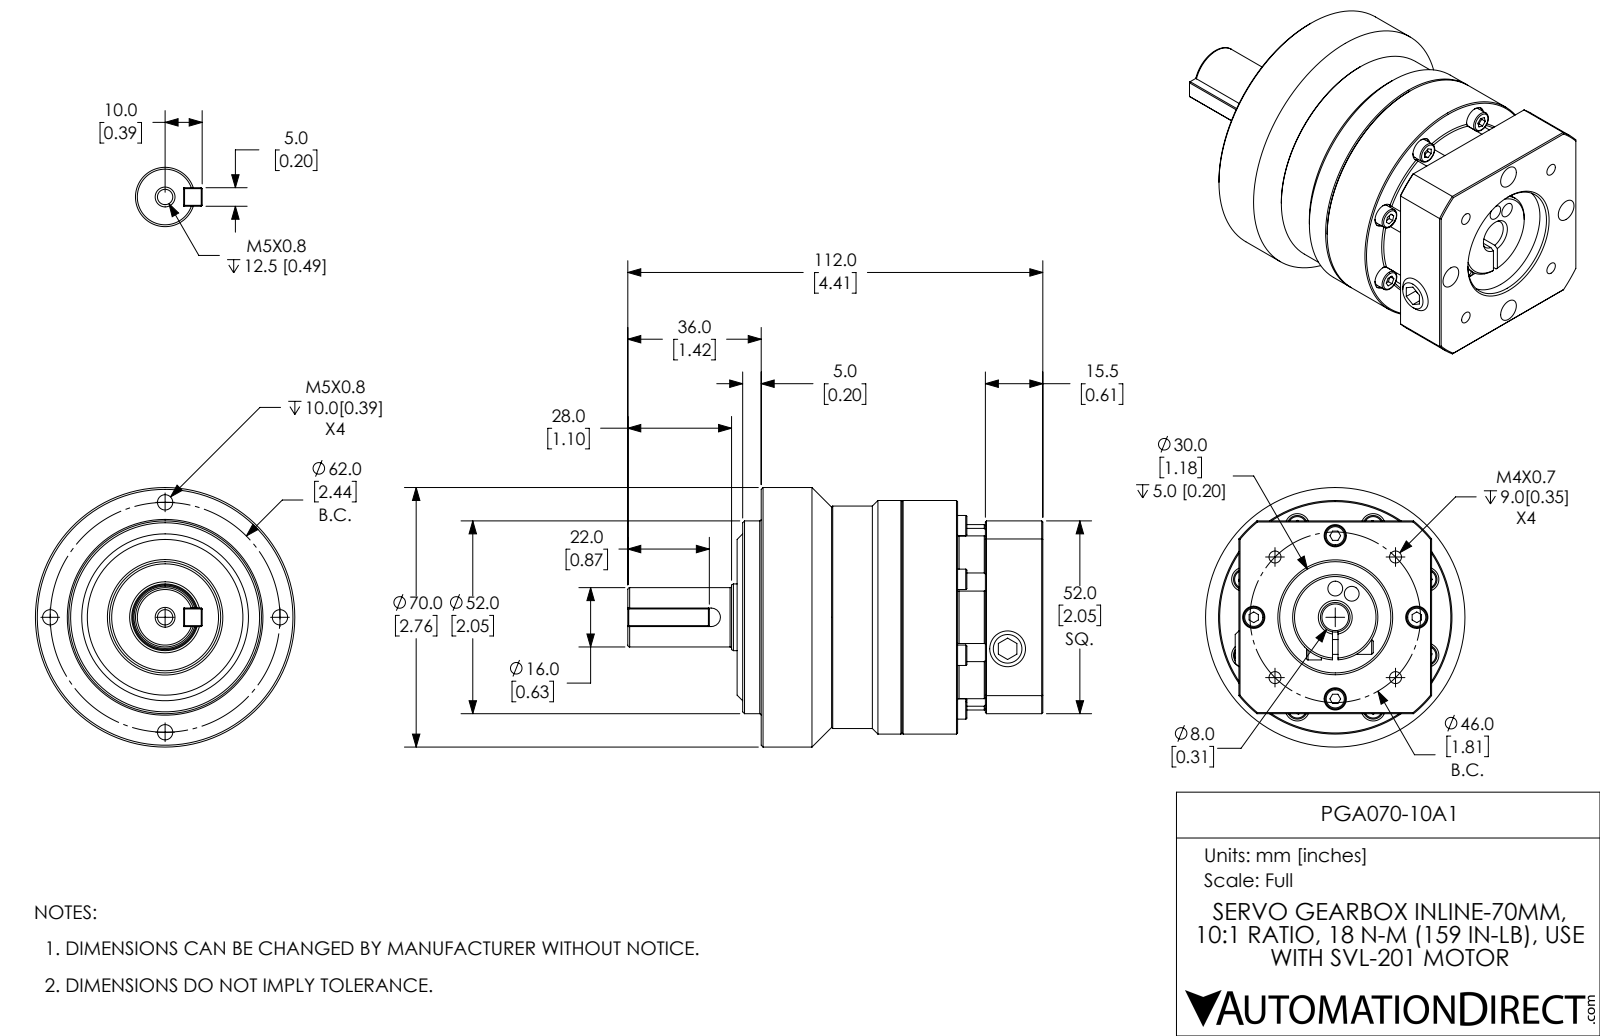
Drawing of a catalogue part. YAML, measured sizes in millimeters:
part_name: "PGA070-10A1"
step_written_by: "SolidWorks 2019 (CONFIG_CONTROL_DESIGN)"
units: millimeters
bodies: {solids: 1, faces: 447, planar: 176, cylindrical: 117, other: 154}
overall_size: [112, 70, 70]
volume: 234000
surface_area: 33960
round_holes:
  - {diameter: 6.5, count: 8}
  - {diameter: 4.1, count: 5}
  - {diameter: 3.3, count: 4}
  - {diameter: 6, count: 4}
  - {diameter: 4, count: 2}
  - {diameter: 8, count: 2}
  - {diameter: 4.5, count: 1}
  - {diameter: 30, count: 1}
  - {diameter: 34, count: 1}
round_bosses_or_shafts:
  - {diameter: 5.5, count: 12}
  - {diameter: 70, count: 1}
  - {diameter: 63, count: 1}
  - {diameter: 60, count: 1}
  - {diameter: 52, count: 1}
  - {diameter: 23, count: 1}
  - {diameter: 18, count: 1}
  - {diameter: 16, count: 1}
partial_cylinders:
  - {radius: 2.5, count: 1}
  - {radius: 4, count: 1}
  - {radius: 25, count: 1}
  - {radius: 33.5, count: 1}
face_to_face_distances: [76, 15.5, 60.5, 67, 52, 6.5, 5, 82.5, 7.5, 53]
hole_center_spacings: [10.4, 10.6, 12, 17.2, 21.9, 26.7, 27.4, 27.8]
